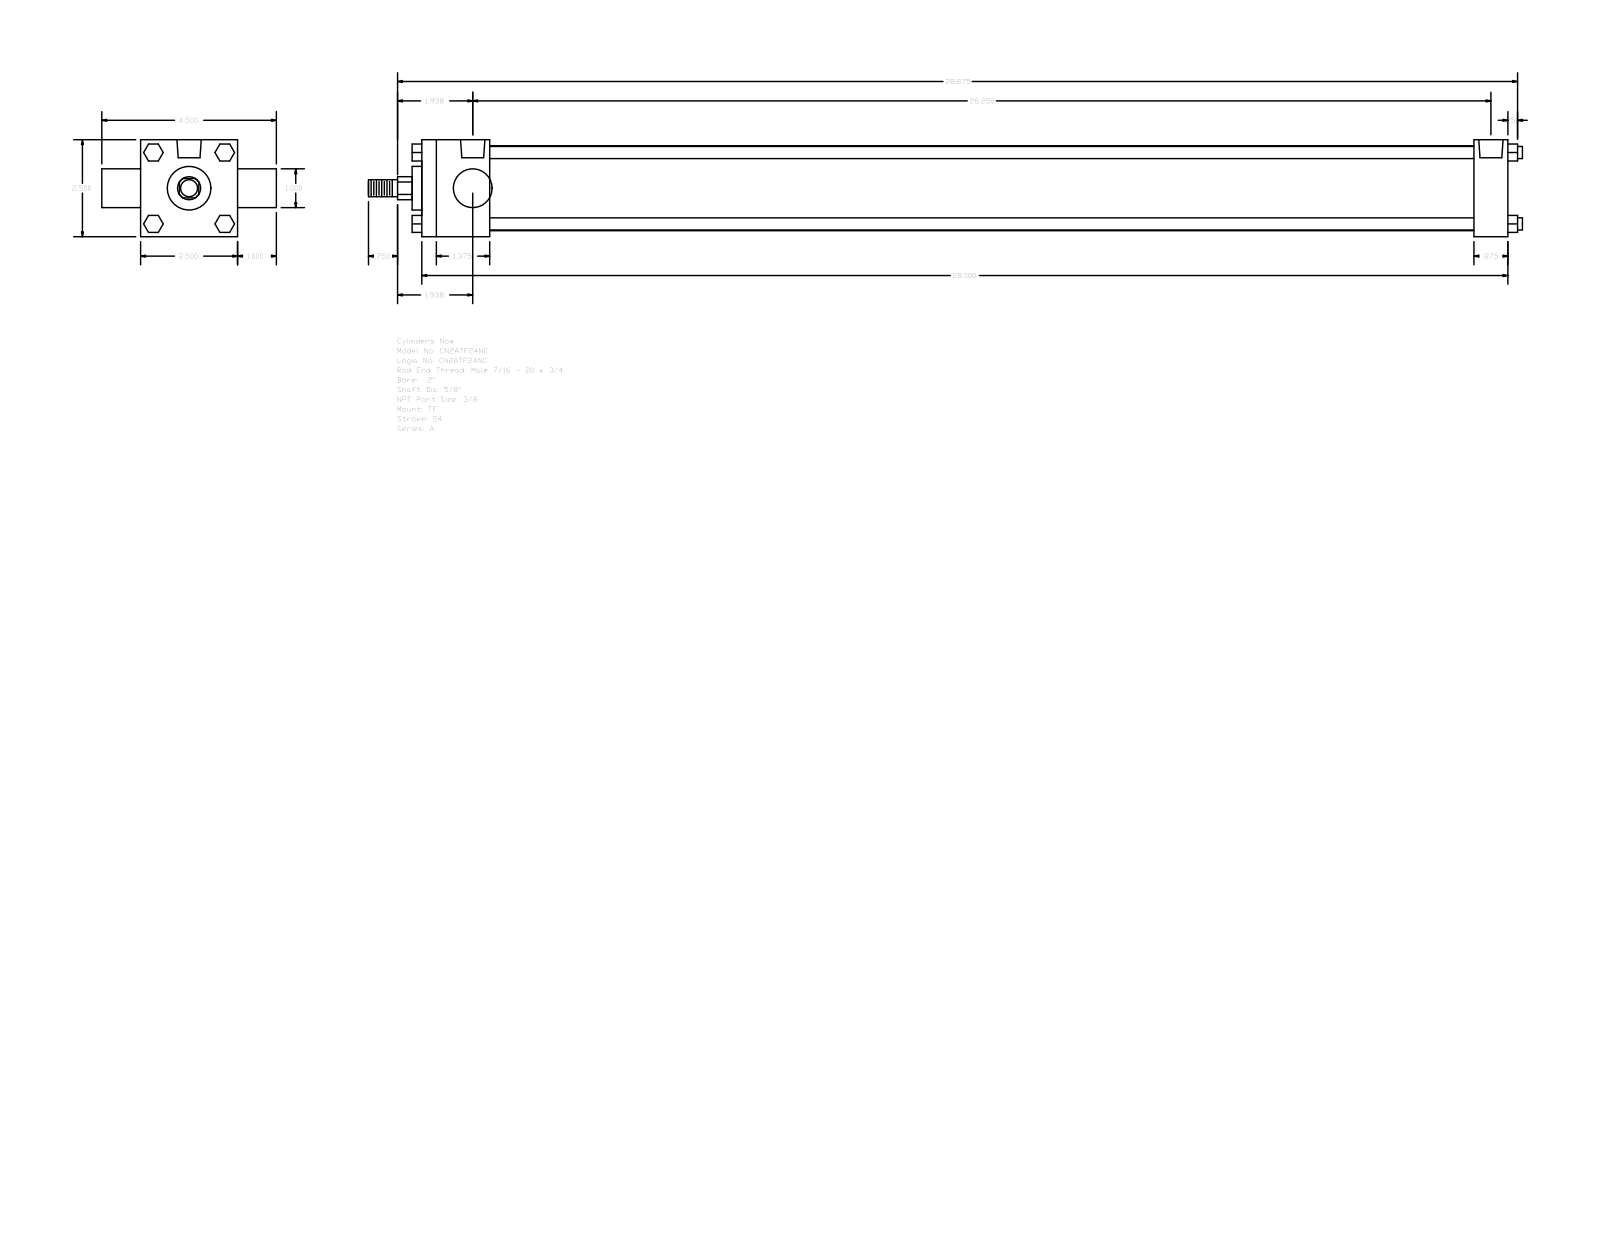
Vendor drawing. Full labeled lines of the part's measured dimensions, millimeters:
Part name (STEP PRODUCT): A_TF__0200_0.625
STEP written by: GSSL Pune (CONFIG_CONTROL_DESIGN)
Units: millimetres
Bodies: 0 solids, 120 faces (92 planar, 28 cylindrical, 0 other)
Overall size (bounding box): 755.65 × 114.3 × 63.5
Round holes (diameter × count): ⌀5.56 ×3, ⌀15.93 ×2
Round bosses / shafts (diameter × count): ⌀7.94 ×4, ⌀55.63 ×1, ⌀28.57 ×1, ⌀25.4 ×1, ⌀15.88 ×1, ⌀11.11 ×1
Partial cylindrical surfaces — rounded edges, fillets, slot ends (radius × count): R7.54 ×1
Main face-to-face distances: 63.5, 711.2, 44.45, 688.97, 644.52, 666.75, 22.23, 25.4, 88.9, 50.8
Hole centre spacings: 3.97, 3.98, 658.8, 662.77, 662.78, 666.75
